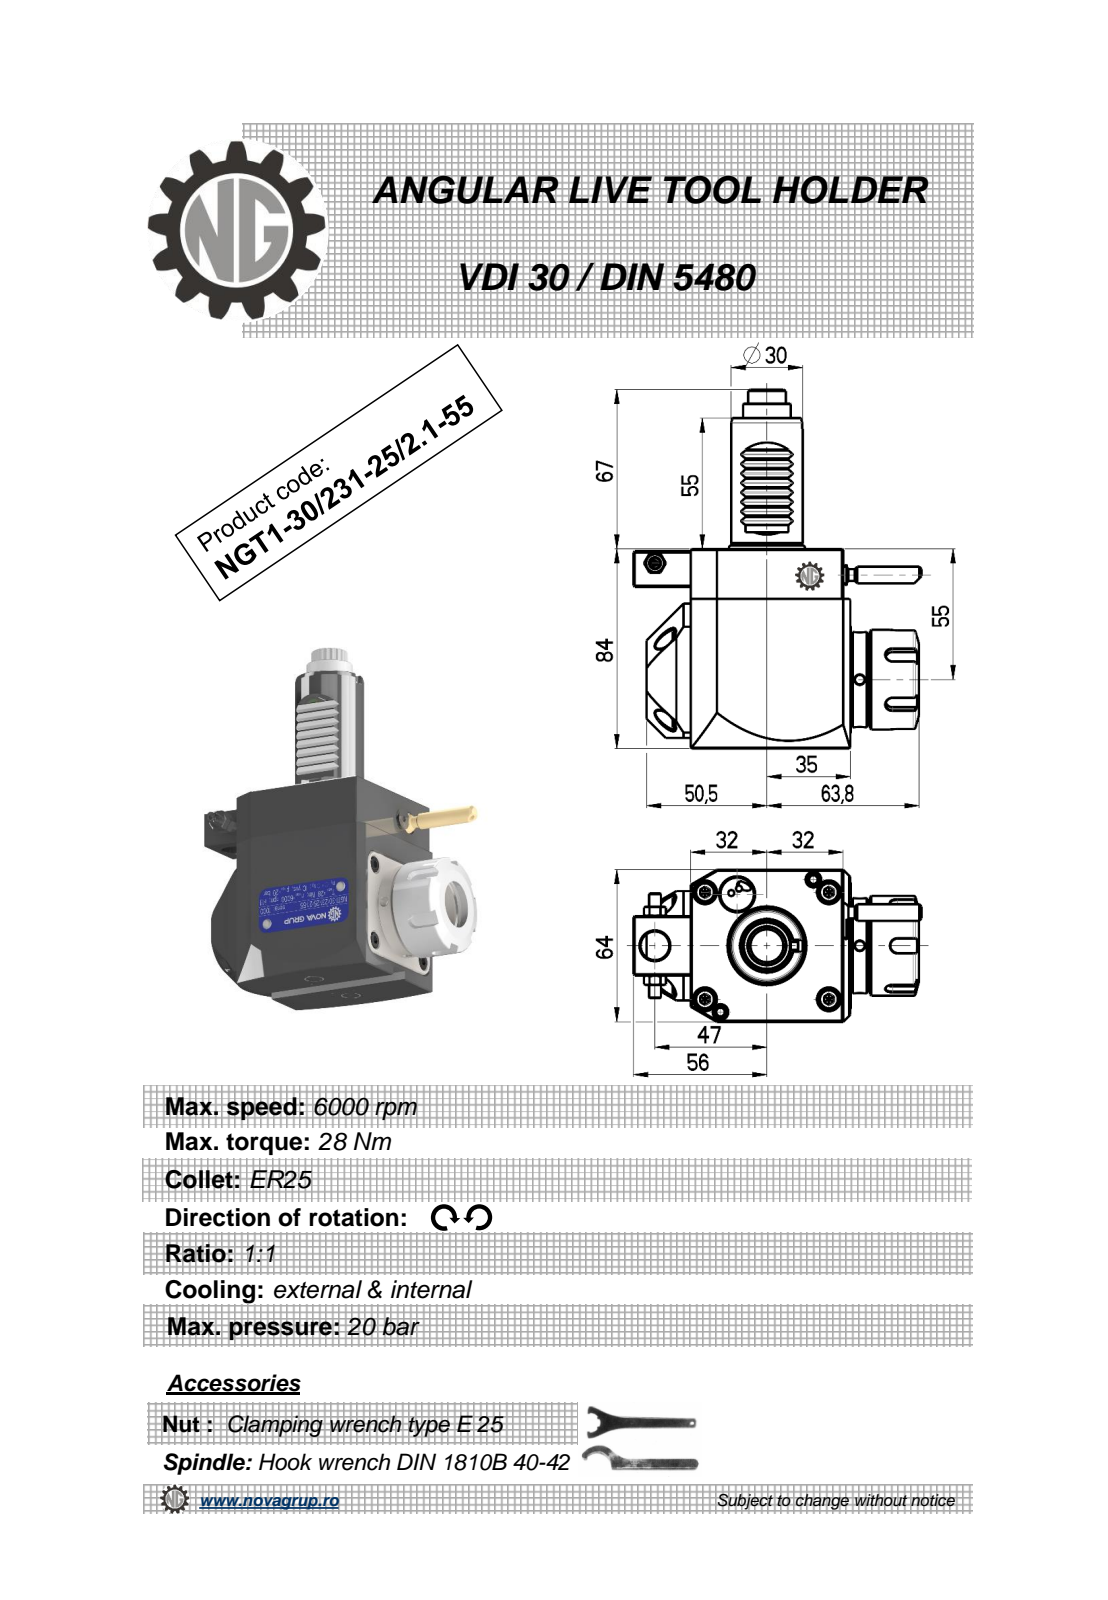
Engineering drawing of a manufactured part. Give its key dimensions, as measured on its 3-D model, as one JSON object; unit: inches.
{"part_name": "NGT1_30_231_25_2_1_55", "step_written_by": "PRO/ENGINEER BY PARAMETRIC TECHNOLOGY CORPORATION, 2010280 (CONFIG_CONTROL_DESIGN)", "units": "inches", "bodies": {"solids": 1, "faces": 498, "planar": 184, "cylindrical": 157, "other": 157}, "overall_size": [5.945, 4.759, 2.583], "volume_in3": 28.21, "surface_area_in2": 73.95, "round_holes": [[0.157, 2], [0.098, 1], [0.118, 1], [0.165, 1], [0.374, 1], [0.472, 1], [0.799, 1]], "round_bosses_or_shafts": [[0.353, 2], [0.197, 2], [1.654, 1], [1.575, 1], [1.299, 1], [1.181, 1], [0.787, 1], [0.276, 1]], "partial_cylinders_radius": [[0.078, 36], [0.01, 12], [0.012, 8], [0.118, 5], [6.299, 2], [0.279, 1], [0.312, 1], [0.512, 1]], "face_to_face_distances": [2.52, 3.307, 2.646, 2.638, 0.126, 0.118, 0.728, 0.02, 3.248, 3.366], "hole_center_spacings": [0.56, 1.818, 1.831, 3.384, 3.895]}
